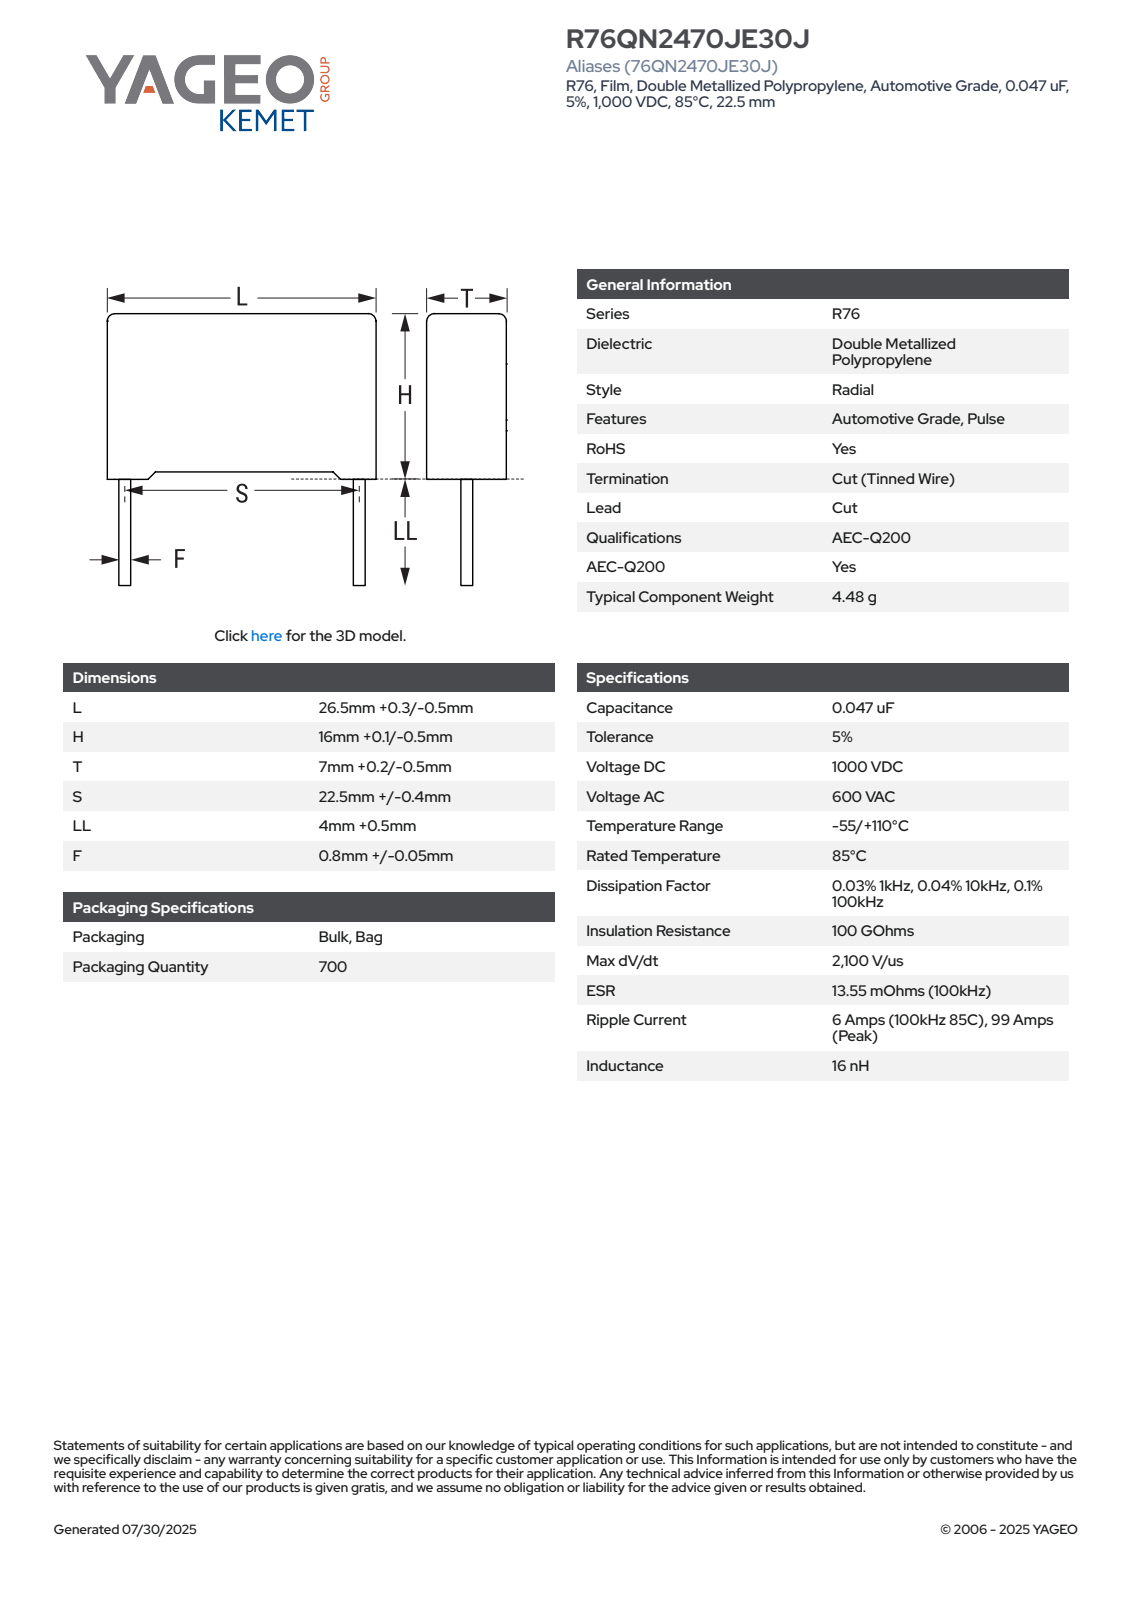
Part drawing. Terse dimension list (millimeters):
name: CFR_RB2_26.5X16X7_L26.8H16.1T7.2S22.5LL4.5F0.85
written by: SolidWorks 2021 (AUTOMOTIVE_DESIGN)
unit: mm
bodies: 4 solids, 85 faces (77 planar, 8 cylindrical, 0 other)
size: 26.8 × 20.6 × 7.21
volume: 2 989 mm³; area: 1 553 mm²
bosses: 2× ⌀0.85
rounds: 4× R0.5
face distances: 7.2, 15.35, 26.8, 15.54, 0.89, 0.56, 0.75, 16.1, 6.31, 5.42
